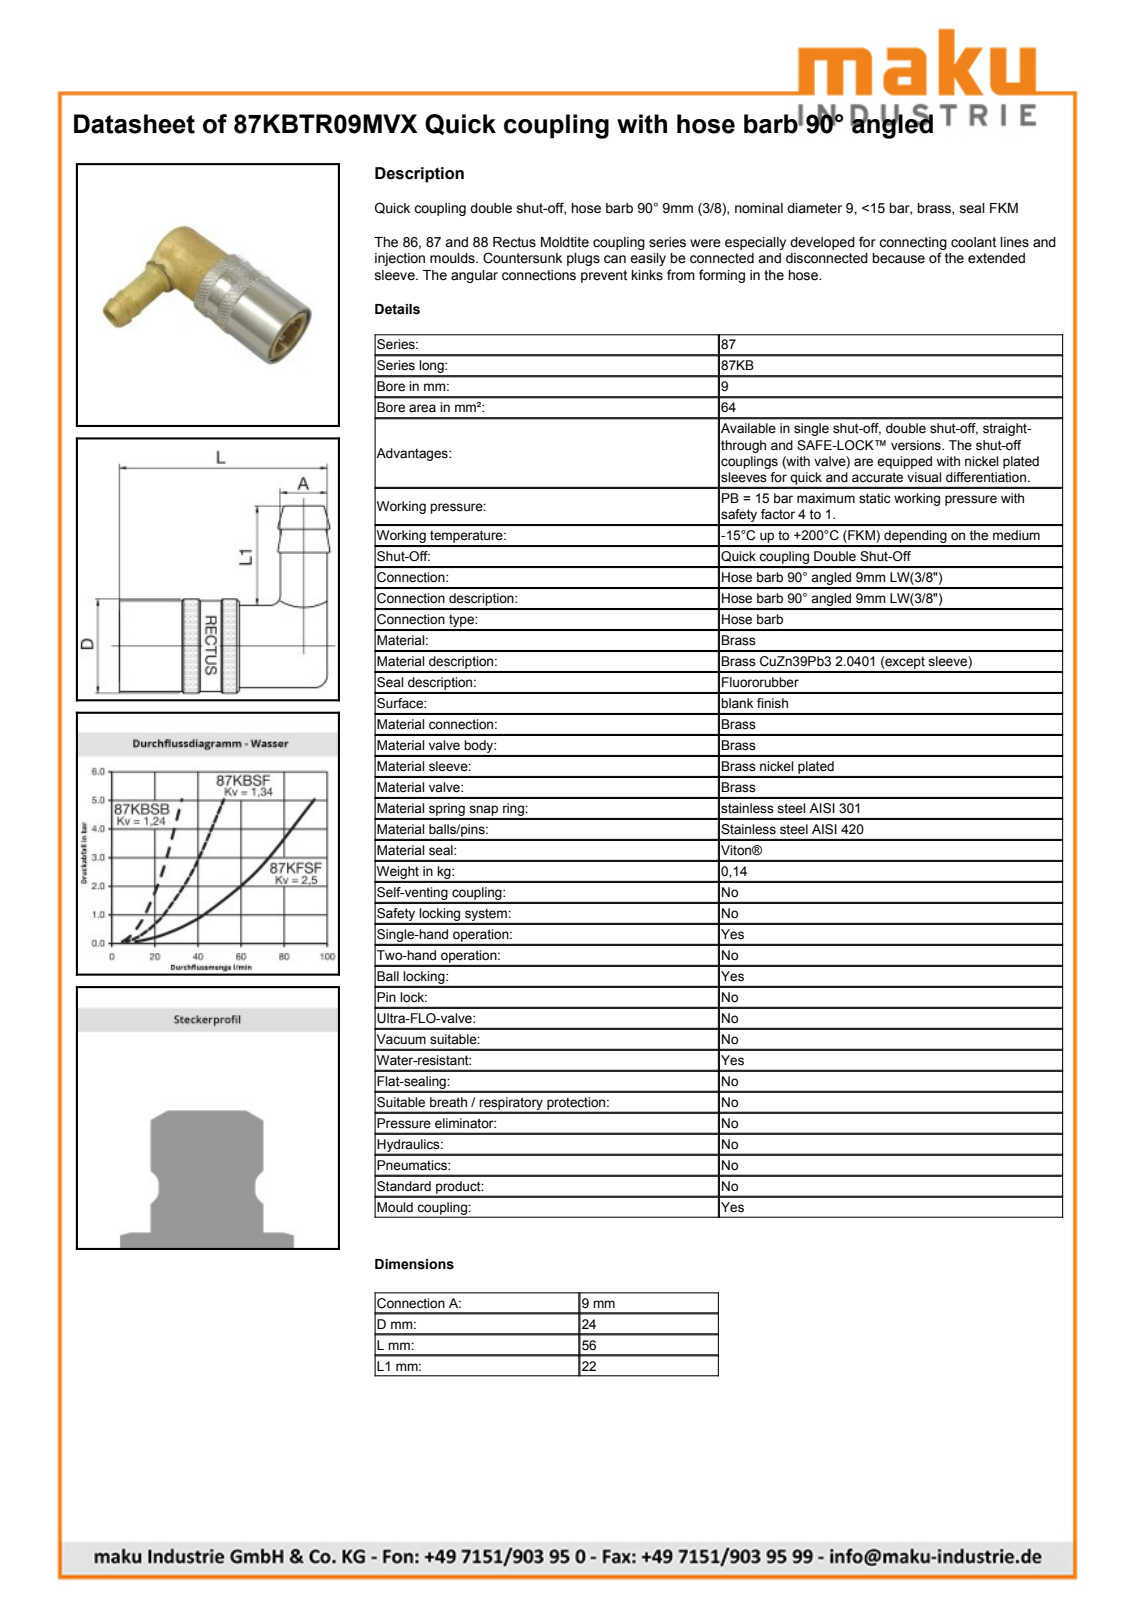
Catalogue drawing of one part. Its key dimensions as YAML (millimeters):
part_name: "87KBTR09MVX"
step_written_by: "Autodesk Inventor 2016 (AUTOMOTIVE_DESIGN)"
units: millimeters
bodies: {solids: 2, faces: 465, planar: 147, cylindrical: 66, other: 252}
overall_size: [56.05, 45.32, 24.15]
volume: 16746
surface_area: 12163
round_holes:
  - {diameter: 7.5, count: 1}
  - {diameter: 9, count: 1}
  - {diameter: 10, count: 1}
  - {diameter: 12.1, count: 1}
  - {diameter: 16.1, count: 1}
  - {diameter: 18.75, count: 1}
  - {diameter: 21.05, count: 1}
  - {diameter: 21.25, count: 1}
round_bosses_or_shafts:
  - {diameter: 24.15, count: 1}
  - {diameter: 23, count: 1}
  - {diameter: 20.3, count: 1}
  - {diameter: 18, count: 1}
  - {diameter: 17.48, count: 1}
  - {diameter: 12, count: 1}
  - {diameter: 9.5, count: 1}
  - {diameter: 8.9, count: 1}
partial_cylinders:
  - {radius: 11.4, count: 1}
face_to_face_distances: [28, 28.05, 56.05, 19, 9.05, 37.05, 0.65, 18.35, 27.4, 55.4]
